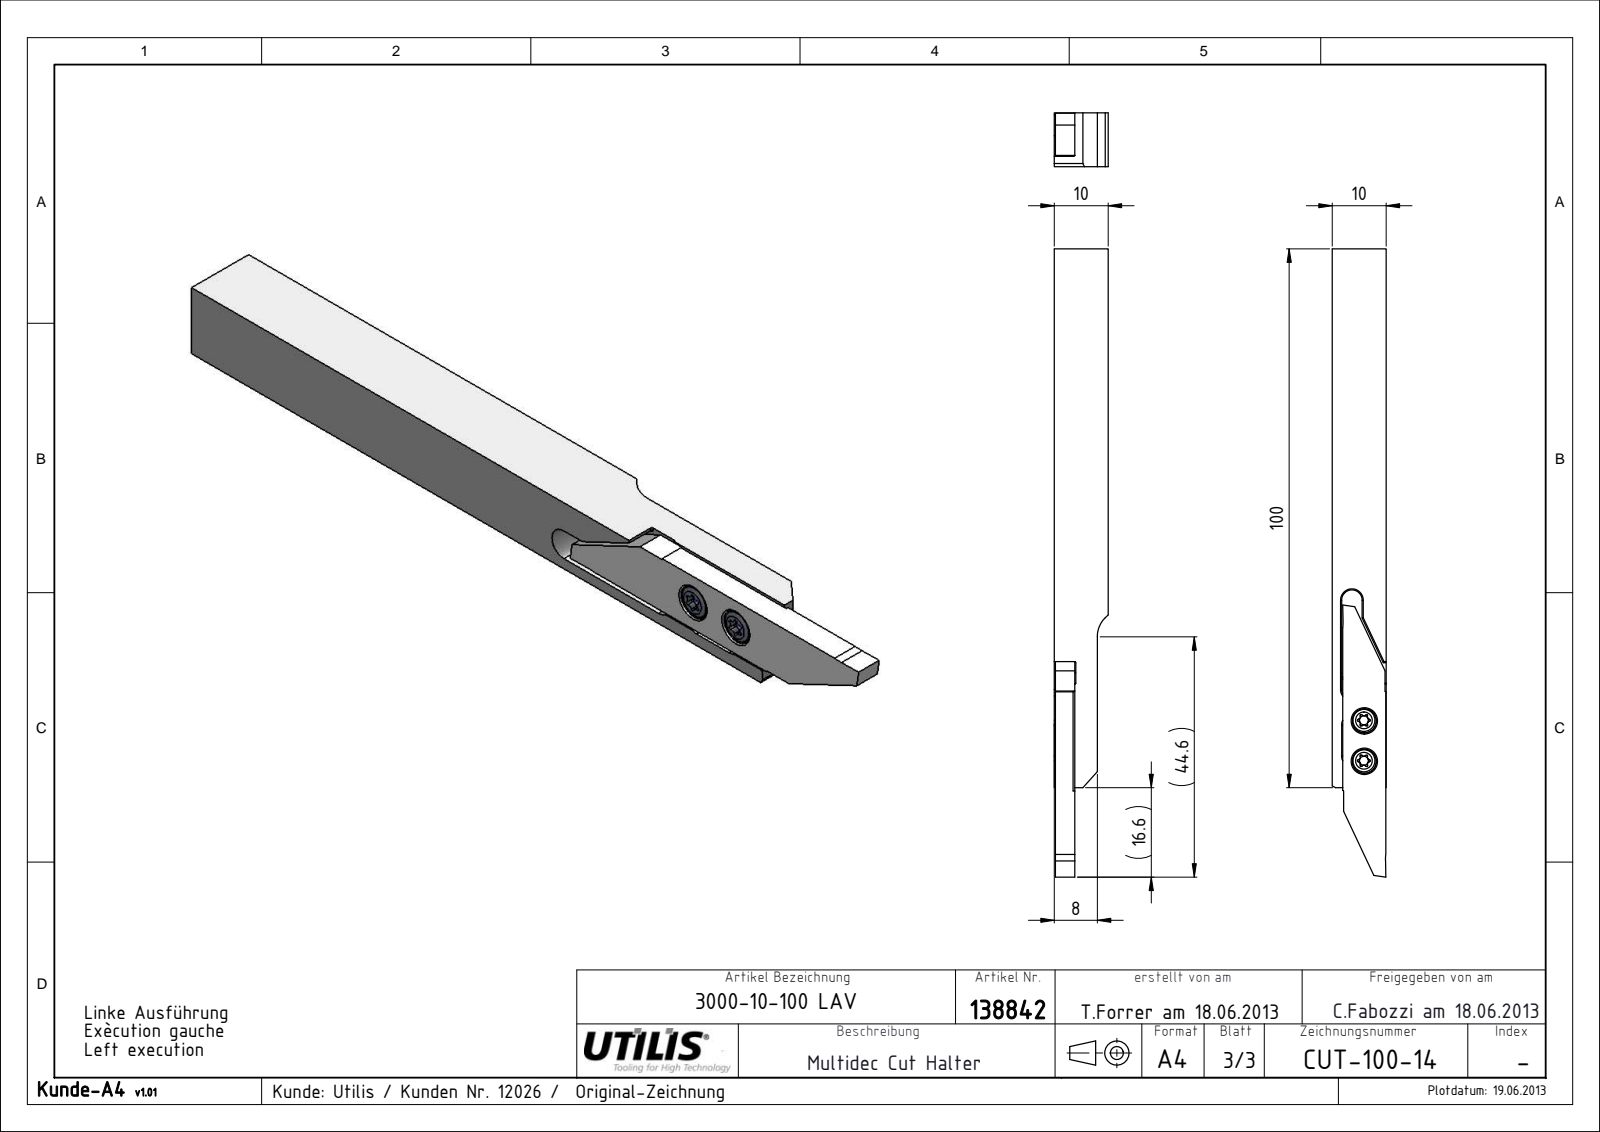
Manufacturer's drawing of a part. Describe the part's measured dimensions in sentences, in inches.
The part is named "CUT-100-14". Its 3-D file was written by "SolidWorks 2016 (AUTOMOTIVE_DESIGN)". It is 1 solid with 45 faces: 33 planar, 8 cylindrical and 4 other. Overall it measures 4.591 by 0.394 by 0.394 inches. Its volume is 0.582 cubic inches and its surface area 7.181 square inches. Partial cylindrical surfaces (rounded edges, fillets, slot ends): 4 of radius 0.083, 2 of radius 0.394, 1 of radius 0.197. The main face-to-face distances are 0.394, 0.315, 0.386, 0.307, 0.079, 0.165, 0.15, 0.142, 0.244, 0.392.
